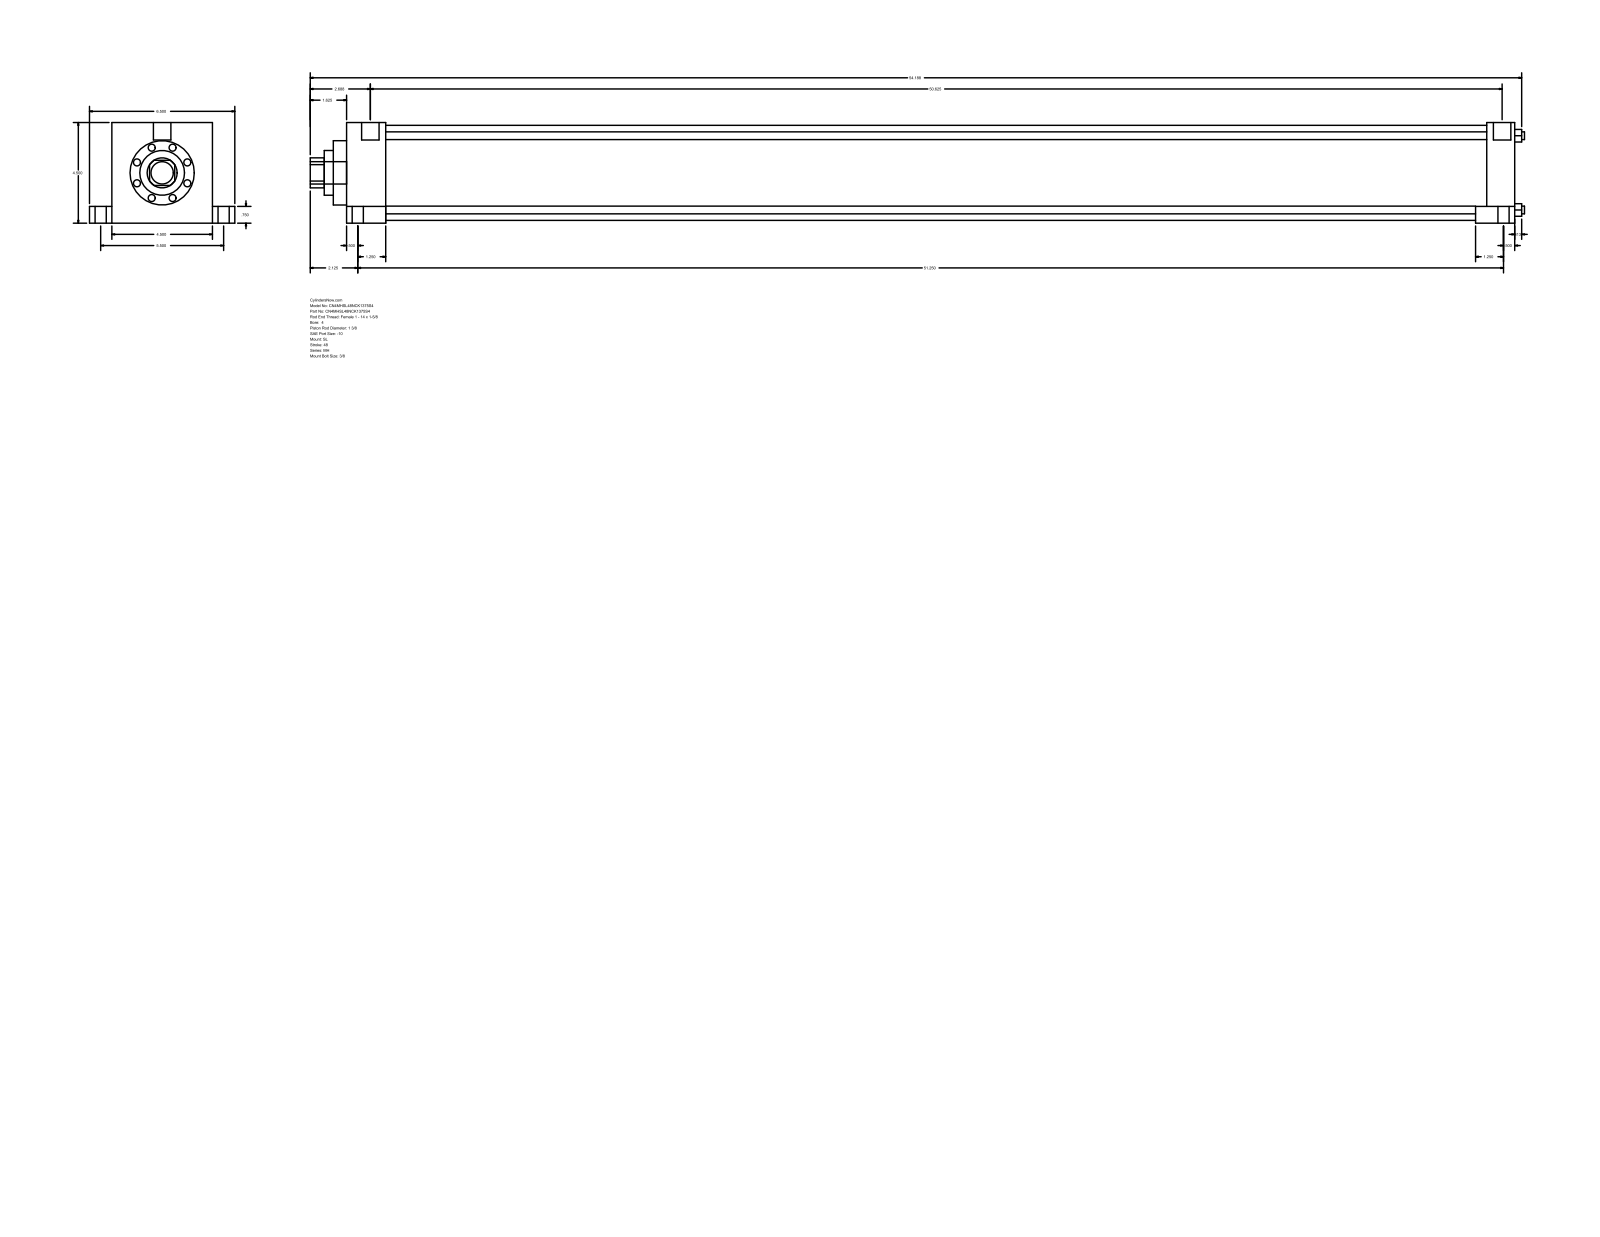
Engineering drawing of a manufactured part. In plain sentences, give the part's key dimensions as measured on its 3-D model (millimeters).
The part is named "MH_SL__0400_1.375". Its 3-D file was written by "GSSL Pune (CONFIG_CONTROL_DESIGN)". It is 0 solids with 110 faces: 77 planar, 33 cylindrical and 0 other. Overall it measures 1379.54 by 165.1 by 114.3 millimeters. Round holes: 4 of diameter 8.76, 1 of diameter 34.92, 1 of diameter 50.8, 1 of diameter 73.03, 1 of diameter 107.95. Round bosses or shafts: 4 of diameter 19.05, 4 of diameter 12.7, 4 of diameter 8.73, 2 of diameter 19.84, 1 of diameter 25.4. Partial cylindrical surfaces (rounded edges, fillets, slot ends): 1 of radius 17.06. The main face-to-face distances are 114.3, 1327.15, 44.45, 1282.7, 1295.4, 1250.95, 31.75, 25.4, 139.7, 19.05. The hole center spacings are 59.62, 84.32, 119.25.
